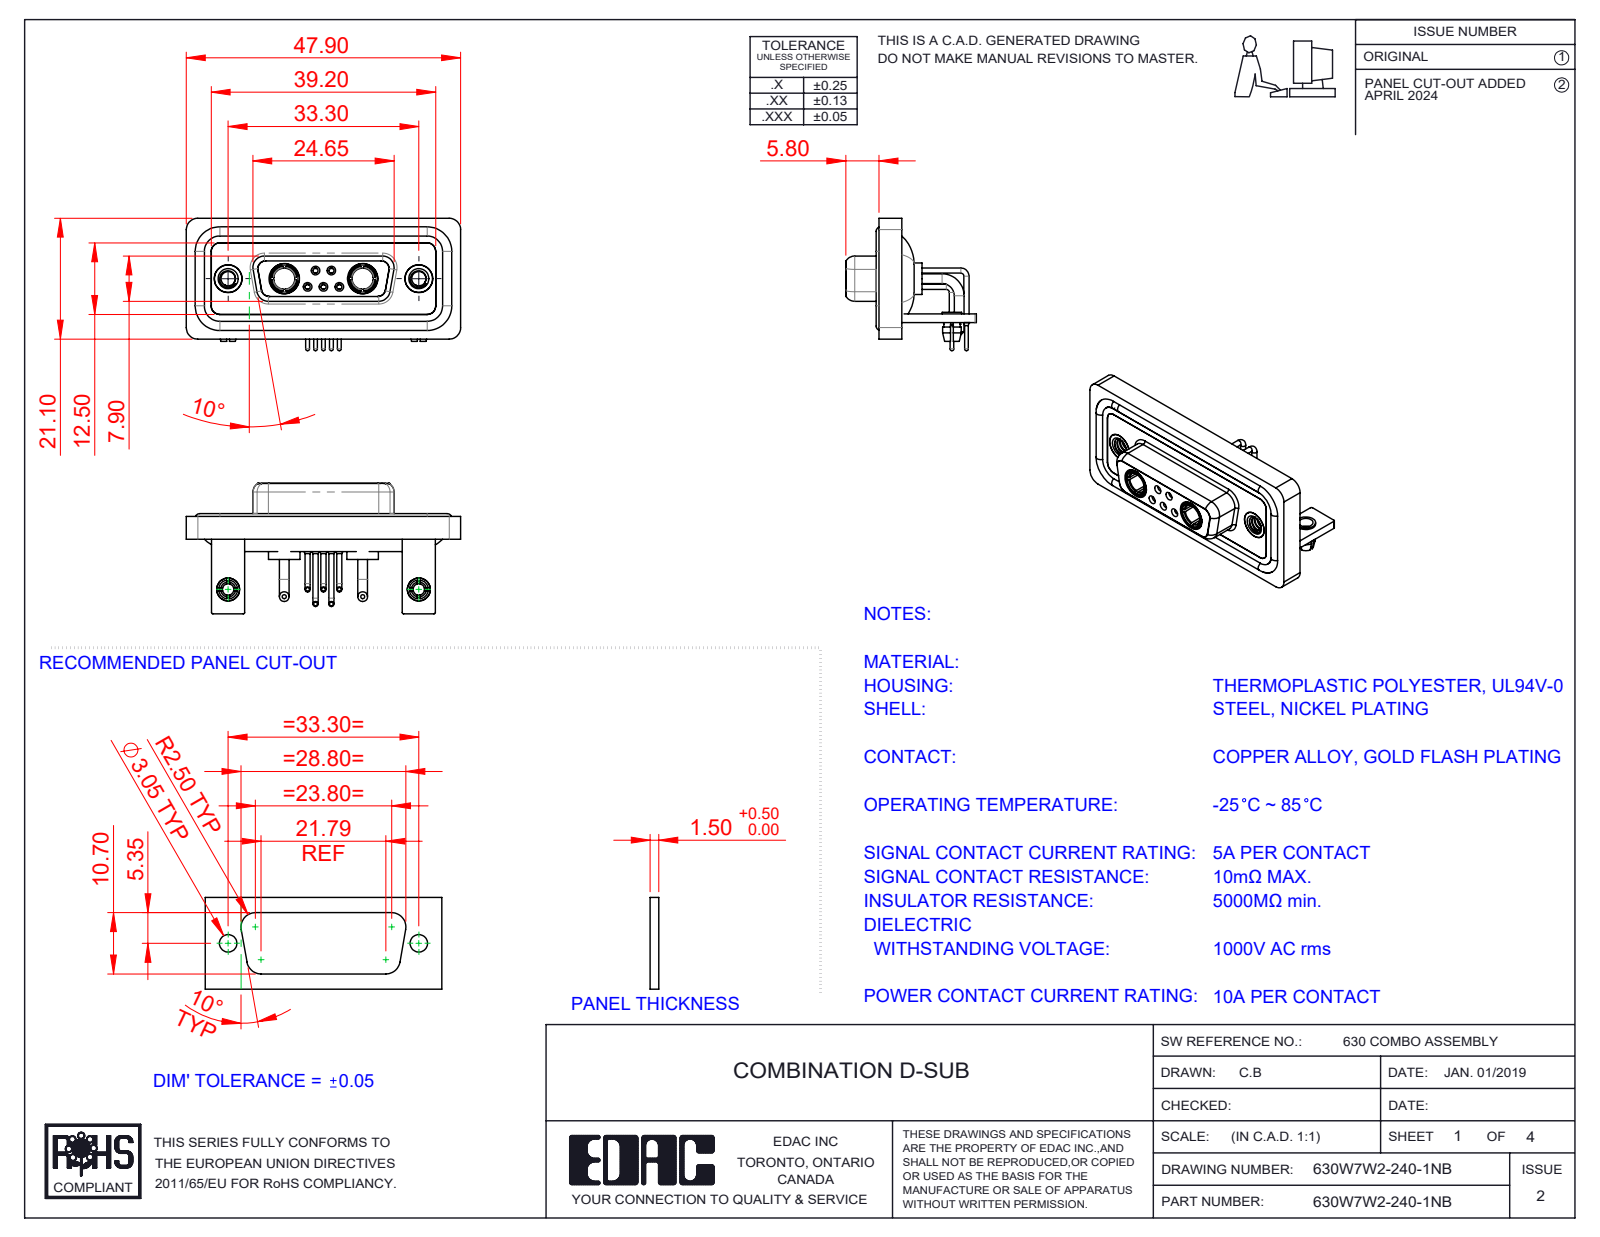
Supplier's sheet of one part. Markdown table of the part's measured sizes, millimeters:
| quantity | value |
| --- | --- |
| part name | 630W7W2-140-1NB; 630Combo Board Lock_50 Contacts; 630Combo Shell Front_15 Contacts; 630Combo Waterproof Housing_15 Contacts (+7 more) |
| STEP written by | SolidWorks 2023 (CONFIG_CONTROL_DESIGN) |
| units | millimeters |
| bodies | 20 solids, 941 faces (306 planar, 407 cylindrical, 228 other) |
| overall size | 47.9 × 23.12 × 22.8 |
| volume | 6 476 mm³ |
| surface area | 11 053 mm² |
| round holes (diameter × count) | 2 × 7, 0.9 × 5, 1.1 × 5, 1.5 × 5, 2.5 × 4, 4.85 × 4, 1.6 × 3, 1.7 × 2, 3.2 × 2, 3.7 × 2, 4 × 2, 4.05 × 2 |
| round bosses / shafts (diameter × count) | 1.6 × 6, 0.9 × 5, 0.65 × 5, 1.7 × 4, 5.5 × 2, 5.2 × 2, 4.96 × 2, 4.95 × 2 |
| partial cylindrical surfaces (radius × count) | 2 × 21, 1.5 × 18, 0.25 × 16, 1.35 × 12, 1.6 × 8, 0.5 × 5, 0.6 × 4, 0.65 × 4 |
| main face-to-face distances | 0.4, 2.9, 1.5, 1.8, 3.7, 1.1, 4.1, 1.6, 2.5, 1.4 |
| hole center spacings | 3.16, 2.77, 9.8, 23.5, 33.3, 4.31, 4.33, 5.03 |
